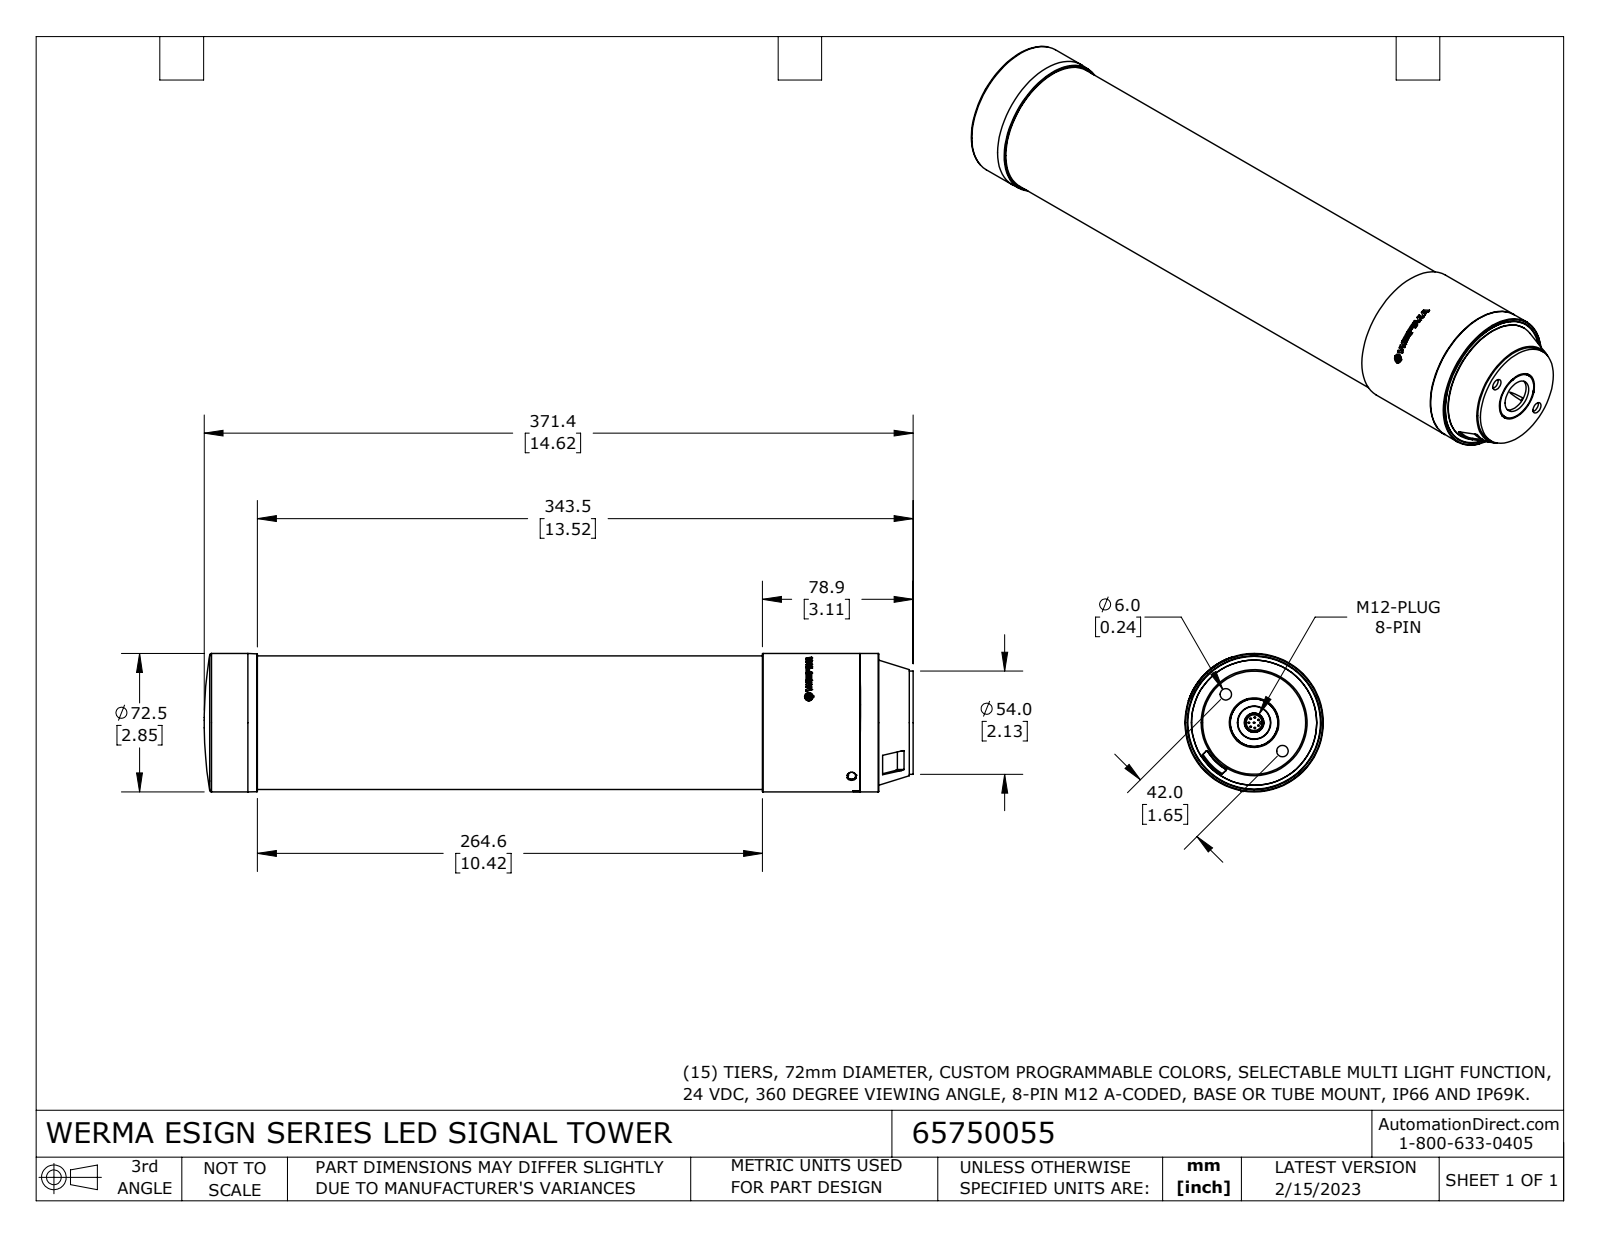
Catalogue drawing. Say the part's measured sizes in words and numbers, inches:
The part is named "65750055". Its 3-D file was written by "SolidWorks 2021 (CONFIG_CONTROL_DESIGN)". It is 1 solid with 268 faces: 110 planar, 97 cylindrical and 61 other. Overall it measures 14.621 by 2.854 by 2.854 inches. Its volume is 86.44 cubic inches and its surface area 143.7 square inches. Round holes: 2 of diameter 0.236, 1 of diameter 0.327, 1 of diameter 0.689, 1 of diameter 1.024. Round bosses or shafts: 8 of diameter 0.031, 1 of diameter 2.854, 1 of diameter 2.756, 1 of diameter 2.126, 1 of diameter 0.98, 1 of diameter 0.173. Partial cylindrical surfaces (rounded edges, fillets, slot ends): 12 of radius 0.01, 2 of radius 0.079, 2 of radius 0.08, 2 of radius 0.099, 1 of radius 0.009, 1 of radius 0.011, 1 of radius 0.016, 1 of radius 0.024. The main face-to-face distances are 0.079, 0.719, 0.64, 1.004, 0.925, 0.285, 1.02, 0.63, 0.709, 0.295. The hole center spacings are 0.827, 1.654.
